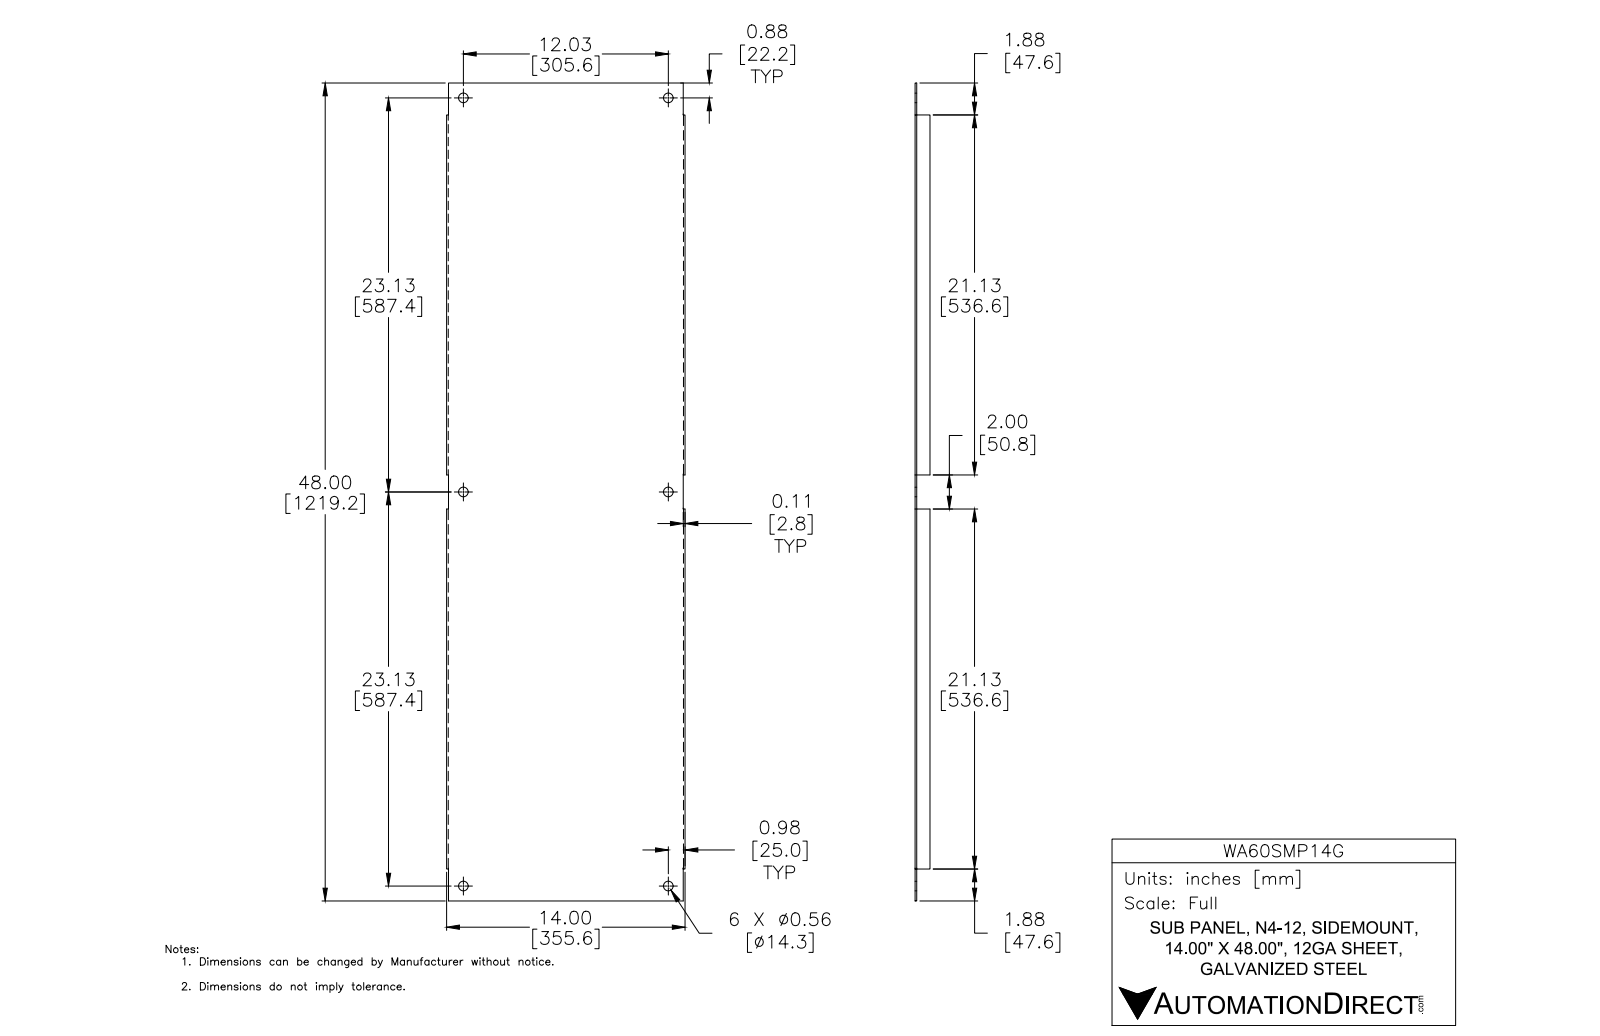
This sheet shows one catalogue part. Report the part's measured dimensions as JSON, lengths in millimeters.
{"part_name": "WA60SMP14G-WA90SMP20G", "step_written_by": "Autodesk Inventor 2012 (AUTOMOTIVE_DESIGN)", "units": "millimeters", "bodies": {"solids": 1, "faces": 48, "planar": 34, "cylindrical": 14, "other": 0}, "overall_size": [1219.2, 355.6, 22.2], "volume_mm3": 1126000, "surface_area_mm2": 954200, "round_holes": [[14.3, 6]], "partial_cylinders_radius": [[0.4, 2], [2.8, 2]], "face_to_face_distances": [2.4, 353.2, 350.9, 355.6, 19.8, 22.2, 1219.2, 2.8, 352.8, 0.4], "hole_center_spacings": [305.6, 587.4, 587.4, 662.1, 662.1, 1174.8, 1213.8]}
